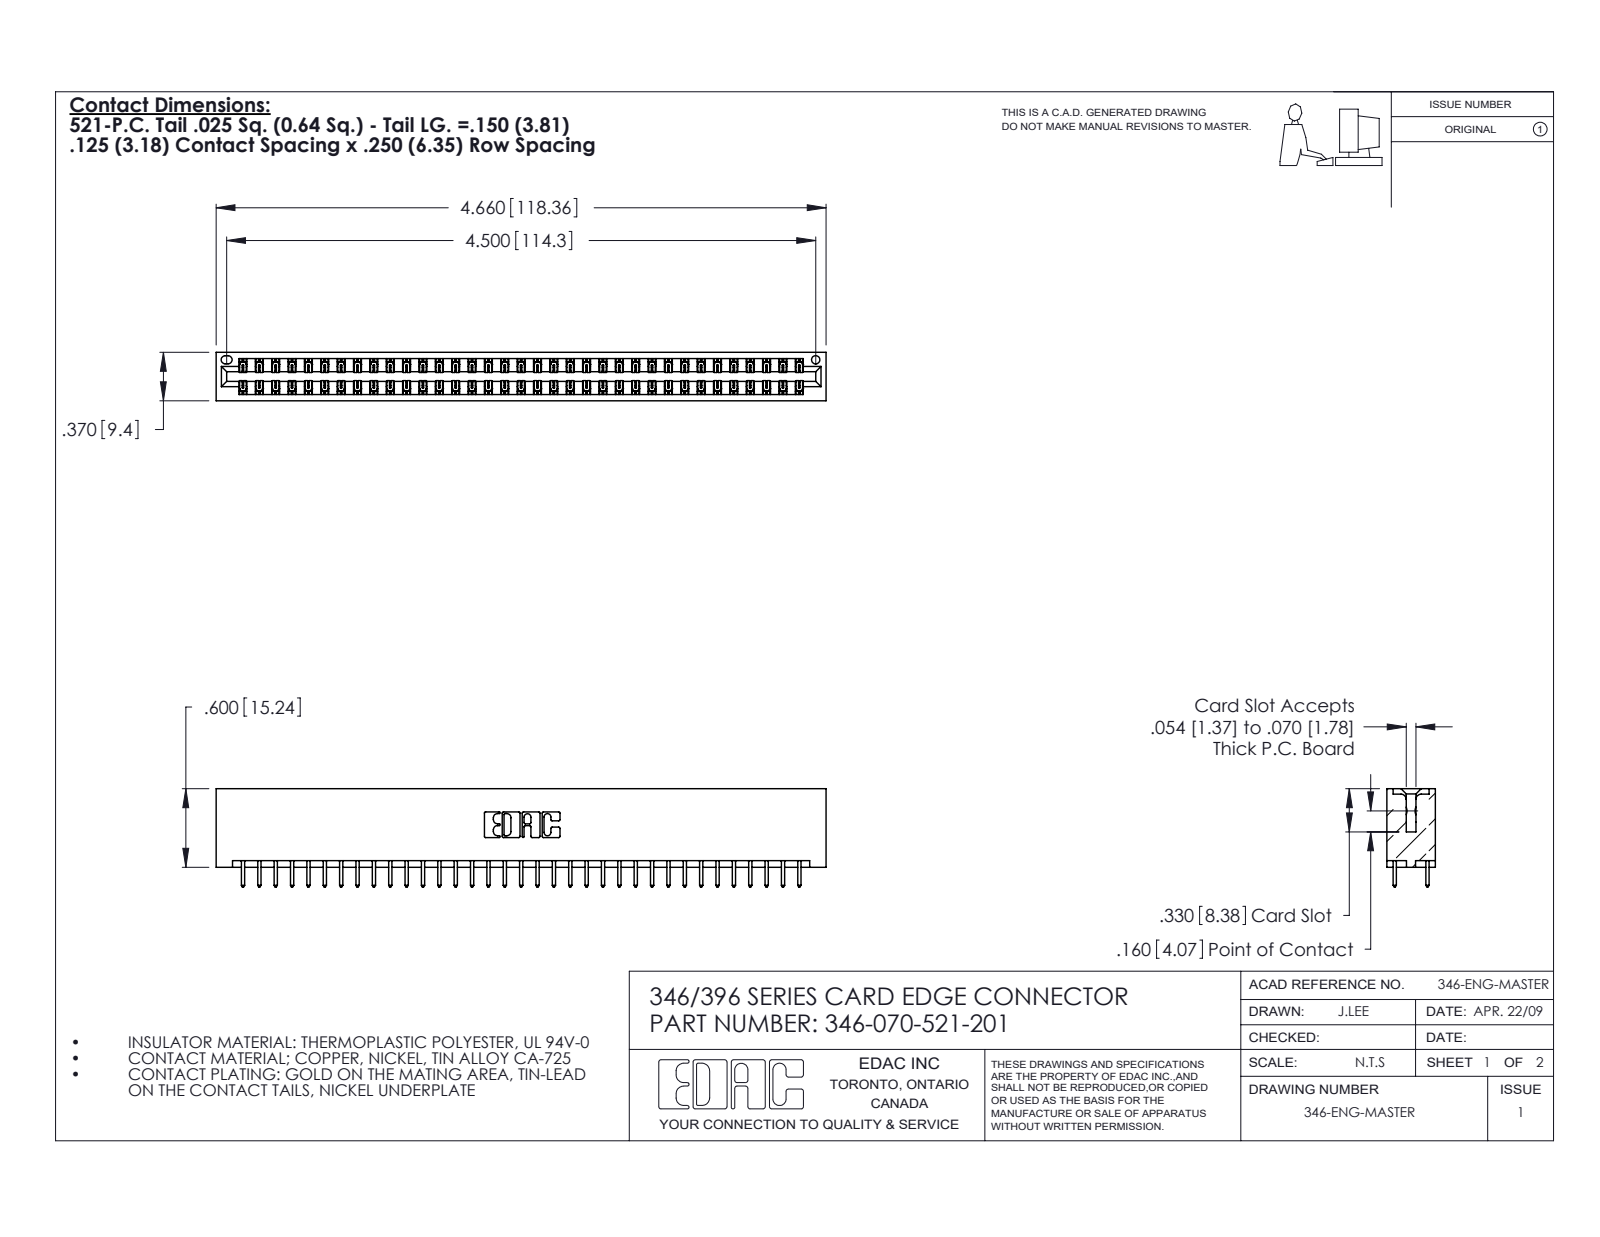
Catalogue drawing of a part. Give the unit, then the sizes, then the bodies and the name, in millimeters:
Units: millimetres
Overall size (bounding box): 118.4 × 19.1 × 9.4
Round holes (diameter × count): ⌀1.6 ×1
Partial cylindrical surfaces — rounded edges, fillets, slot ends (radius × count): R0.2 ×105, R0.3 ×70, R0.3 ×22, R0.2 ×6, R0.8 ×6, R0.7 ×3, R0.4 ×2, R0.6 ×2
Main face-to-face distances: 1.2, 8.2, 6.4, 9.4, 1.8, 7.6, 0.6, 7, 3.8, 5.6
Volume: 12 000 mm³ · Surface area: 16 400 mm²
Bodies: 71 solids, 3754 faces (2522 planar, 1232 cylindrical, 0 other)
Part name (STEP PRODUCT): 346 Part_No Mounting Lugs; 346-070-521-201; 345-292-001_345-293-121
STEP written by: SolidWorks 2020 (CONFIG_CONTROL_DESIGN)
